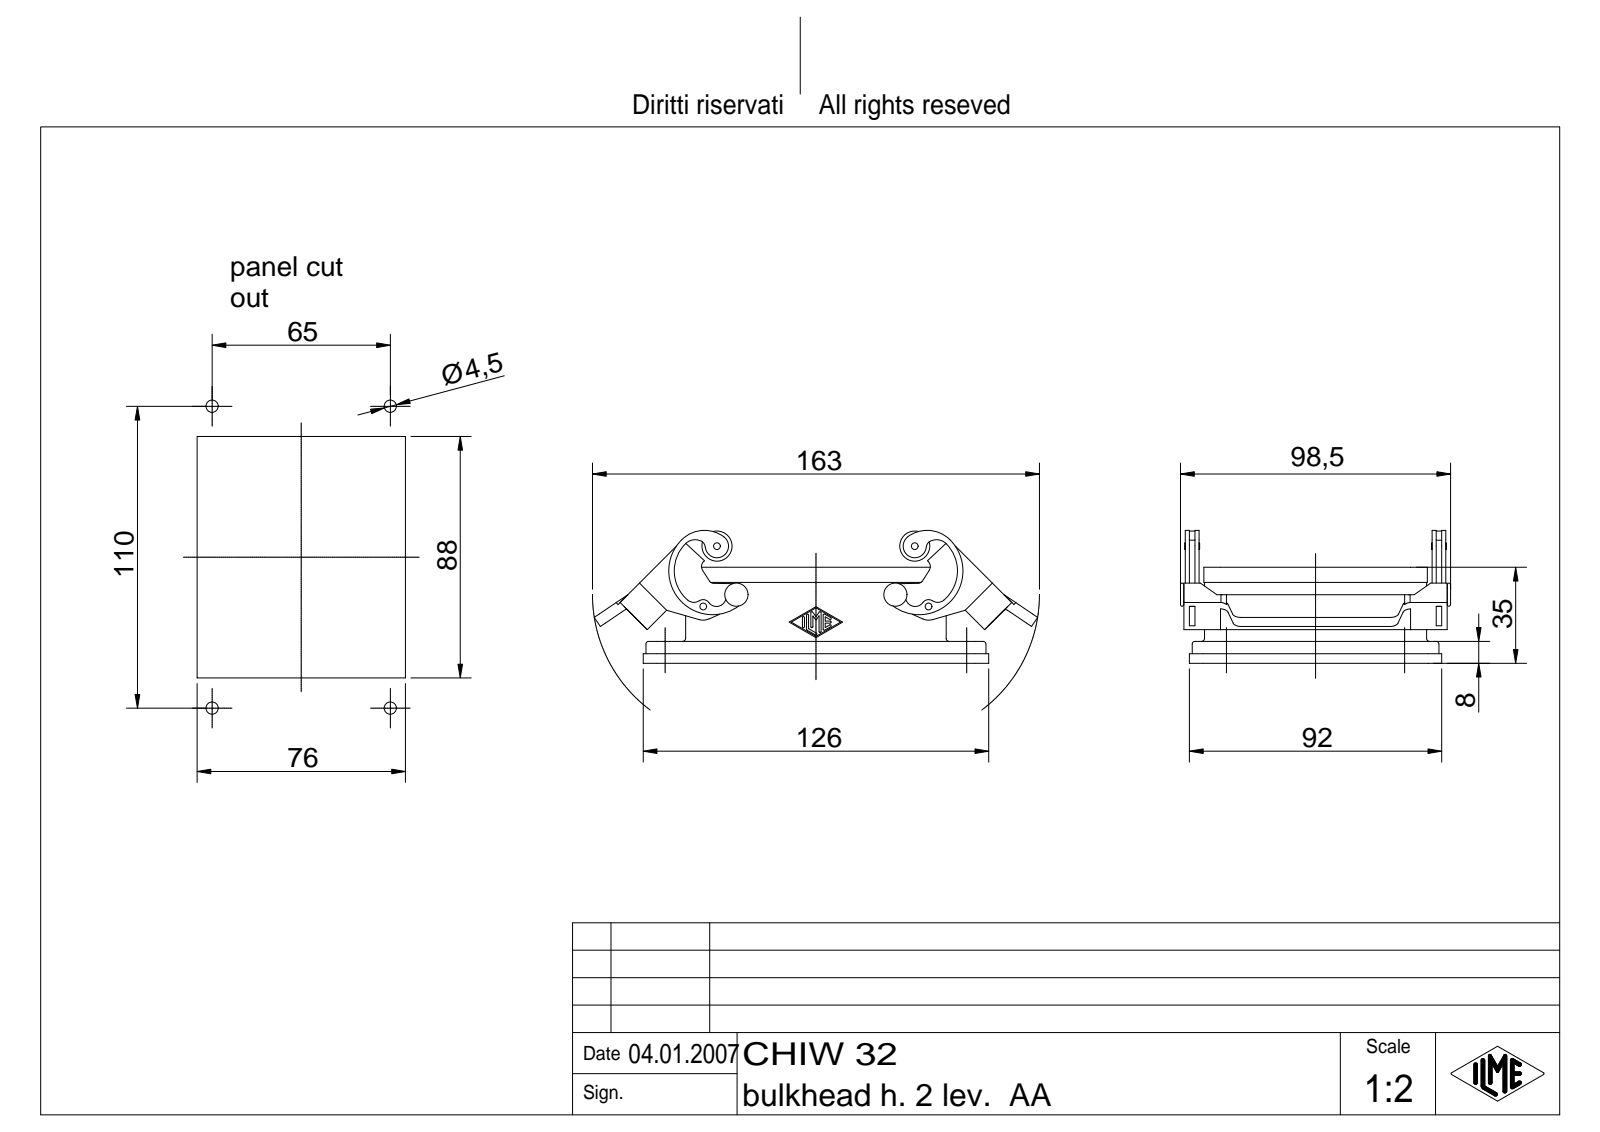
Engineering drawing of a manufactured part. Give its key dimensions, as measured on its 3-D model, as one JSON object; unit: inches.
{"part_name": "CHIW 32", "step_written_by": "Autodesk Inventor 7 (AUTOMOTIVE_DESIGN)", "units": "inches", "bodies": {"solids": 1, "faces": 747, "planar": 212, "cylindrical": 228, "other": 307}, "overall_size": [6.366, 3.878, 1.907], "volume_in3": 6.154, "surface_area_in2": 91.32, "round_holes": [[0.079, 4], [0.097, 4], [0.122, 4], [0.177, 4], [0.181, 4], [0.098, 2]], "round_bosses_or_shafts": [[0.433, 2], [0.197, 2], [0.118, 2]], "partial_cylinders_radius": [[0.015, 14], [0.118, 12], [0.098, 10], [0.039, 9], [0.138, 8], [0.197, 8], [0.236, 8], [0.059, 6]], "face_to_face_distances": [0.118, 3.622, 0.039, 0.157, 3.071, 0.315, 0.128, 0.138, 3.504, 0.335], "hole_center_spacings": [0.641, 0.888, 1.063, 1.274, 1.591, 2.559, 2.6, 3.051]}
